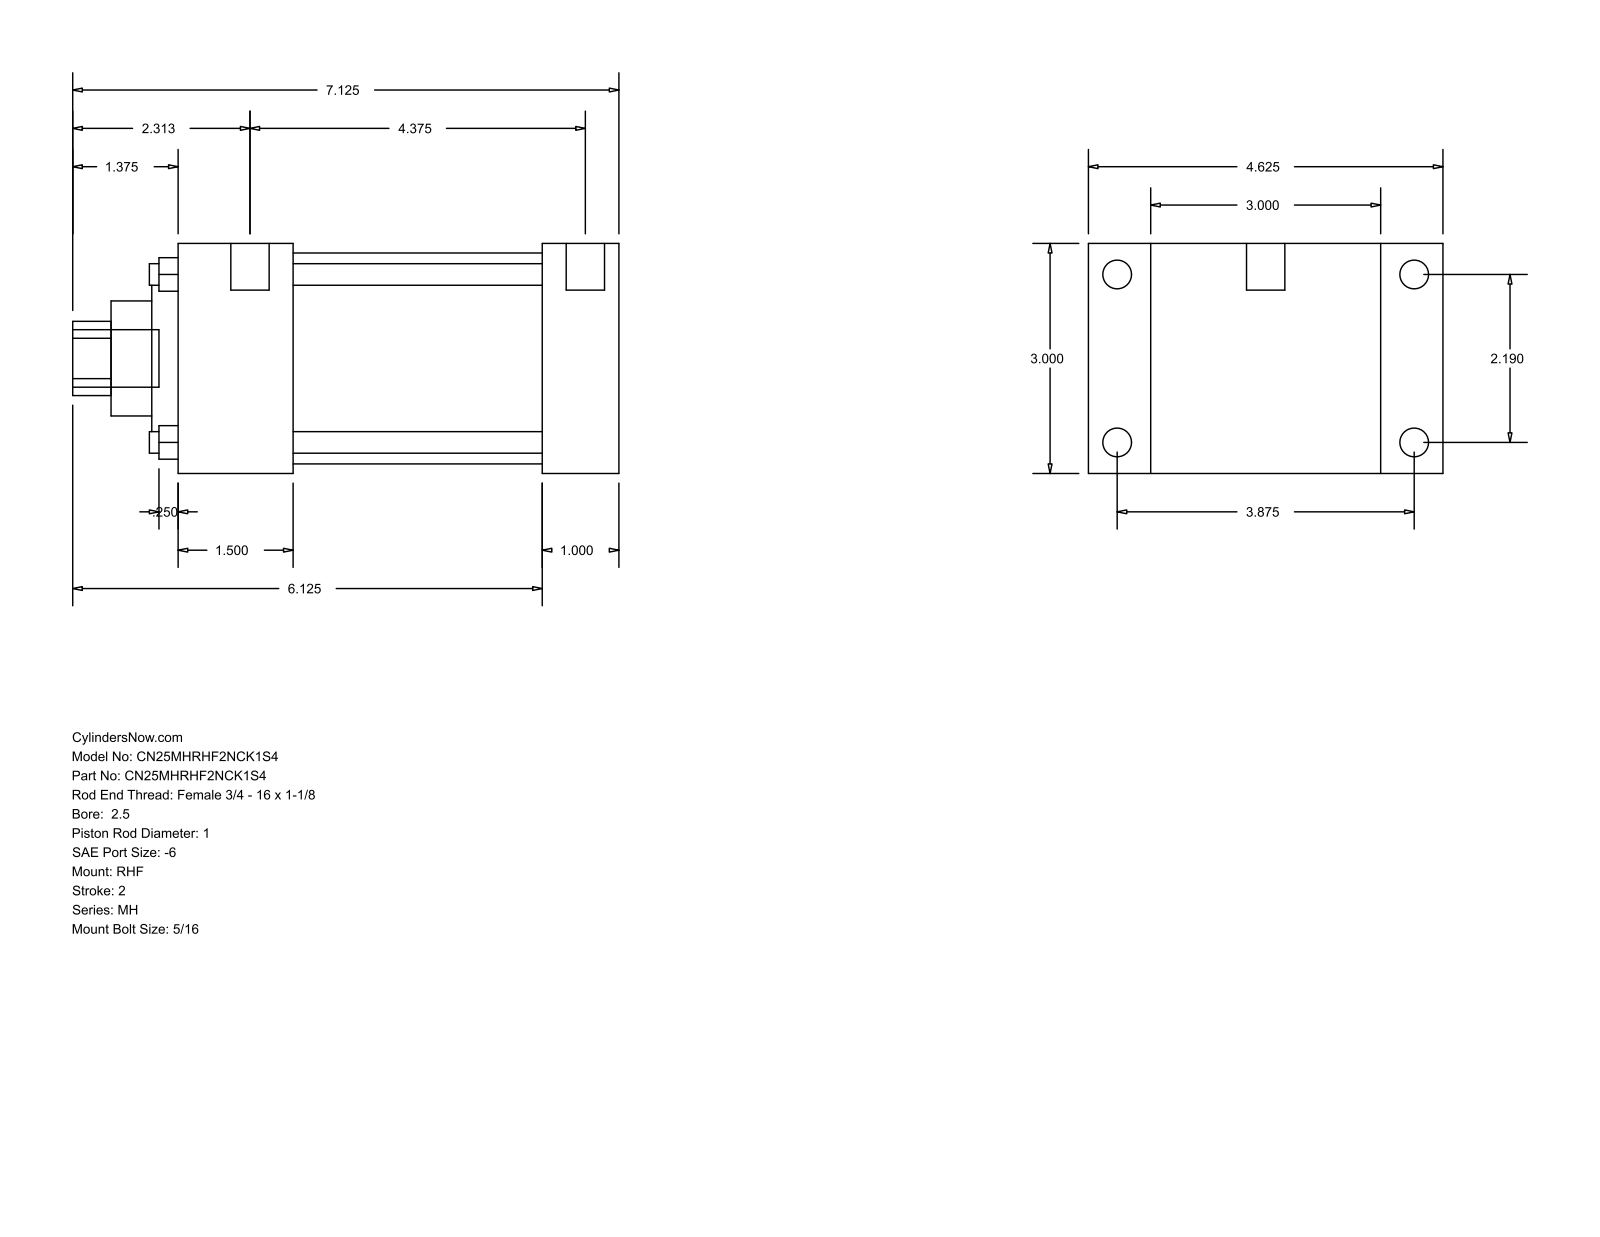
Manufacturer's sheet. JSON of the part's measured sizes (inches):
{"part_name": "MH_RHF__0250_1", "step_written_by": "GSSL Pune (CONFIG_CONTROL_DESIGN)", "units": "inches", "bodies": {"solids": 0, "faces": 90, "planar": 61, "cylindrical": 29, "other": 0}, "overall_size": [7.125, 4.625, 3], "round_holes": [[0.281, 4], [1, 1], [1.5, 1], [2.375, 1], [2.75, 1]], "round_bosses_or_shafts": [[0.375, 4], [0.219, 4], [0.5, 2], [0.75, 1]], "partial_cylinders_radius": [[0.484, 1]], "face_to_face_distances": [3, 1, 0.813, 3.813, 4.75, 5.75, 4.625, 1.5, 3.25, 4.25], "hole_center_spacings": [1.548, 2.19, 3.097]}
